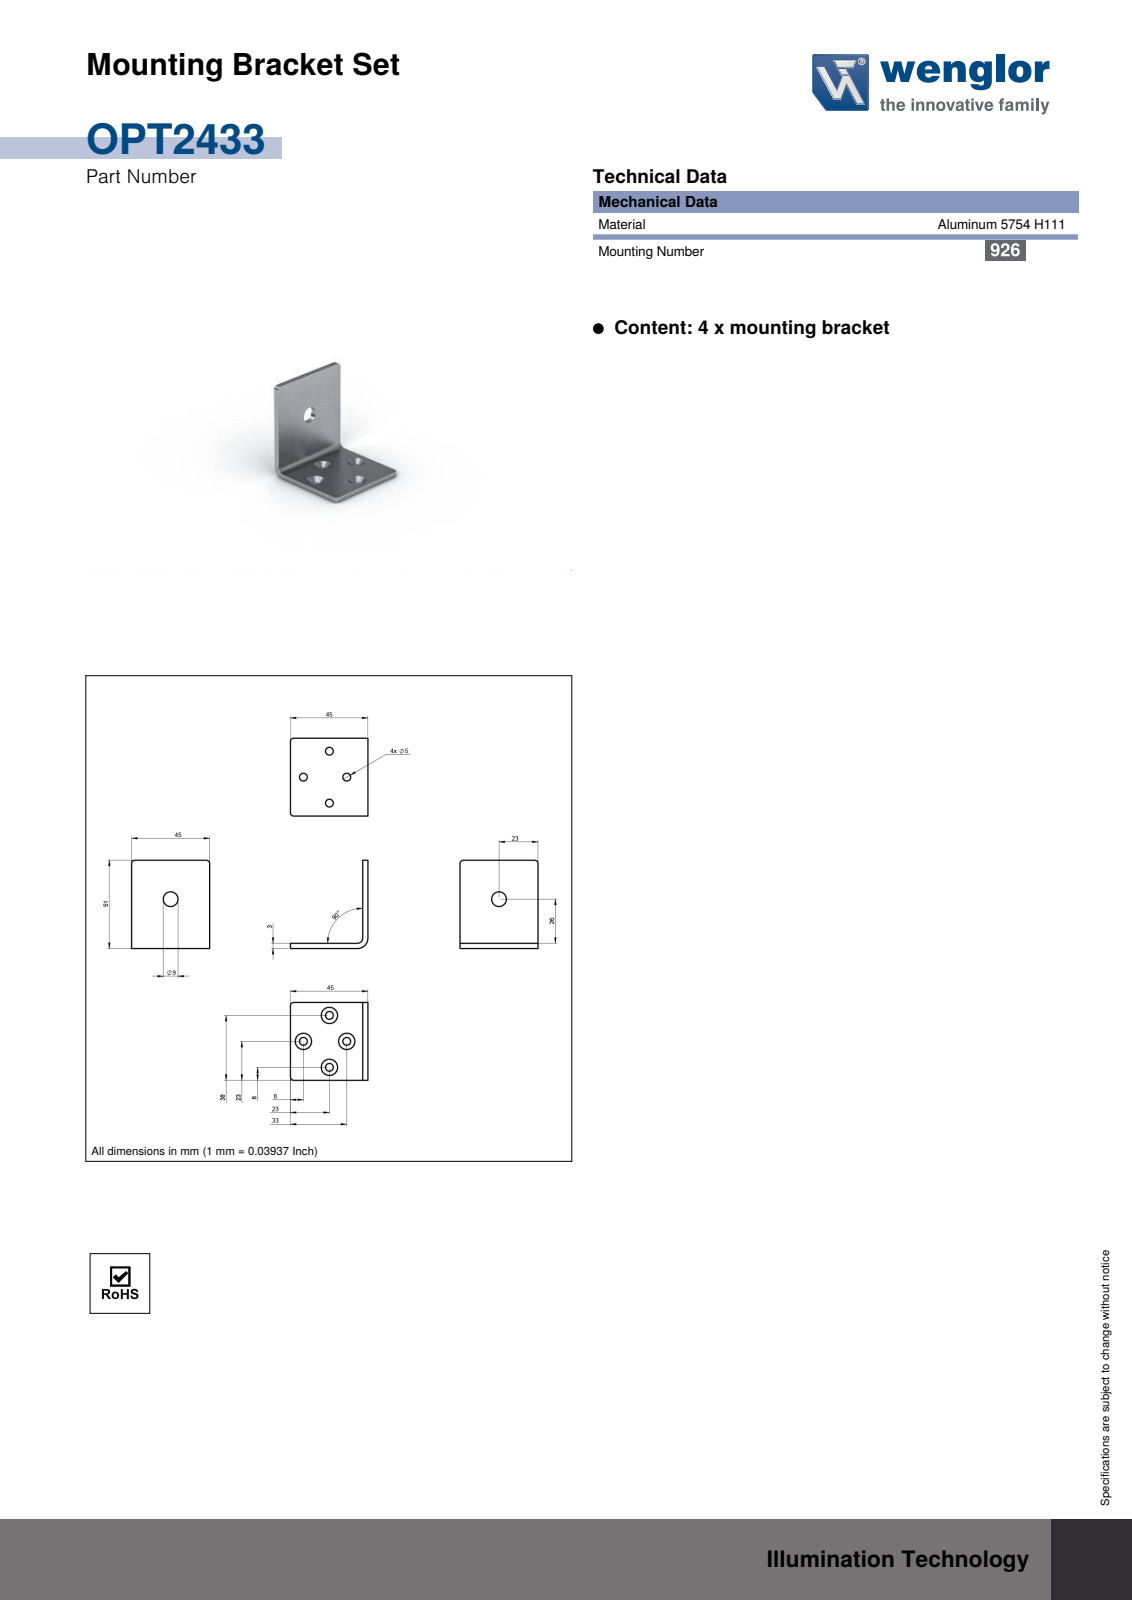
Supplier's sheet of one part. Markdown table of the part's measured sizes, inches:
| quantity | value |
| --- | --- |
| part name | OPT2433 |
| STEP written by | SolidWorks 2021 (AUTOMOTIVE_DESIGN) |
| units | inches |
| bodies | 1 solid, 32 faces (8 planar, 16 cylindrical, 8 other) |
| overall size | 2.008 × 1.772 × 1.76 |
| volume | 0.711 in³ |
| surface area | 13.83 in² |
| round holes (diameter × count) | 0.177 × 4, 0.335 × 1 |
| partial cylindrical surfaces (radius × count) | 0.079 × 4, 0.118 × 1, 0.236 × 1 |
| main face-to-face distances | 0.118, 1.772, 1.76, 1.642, 2.008, 1.89 |
| hole center spacings | 0.71, 0.835, 0.984, 1.181 |
